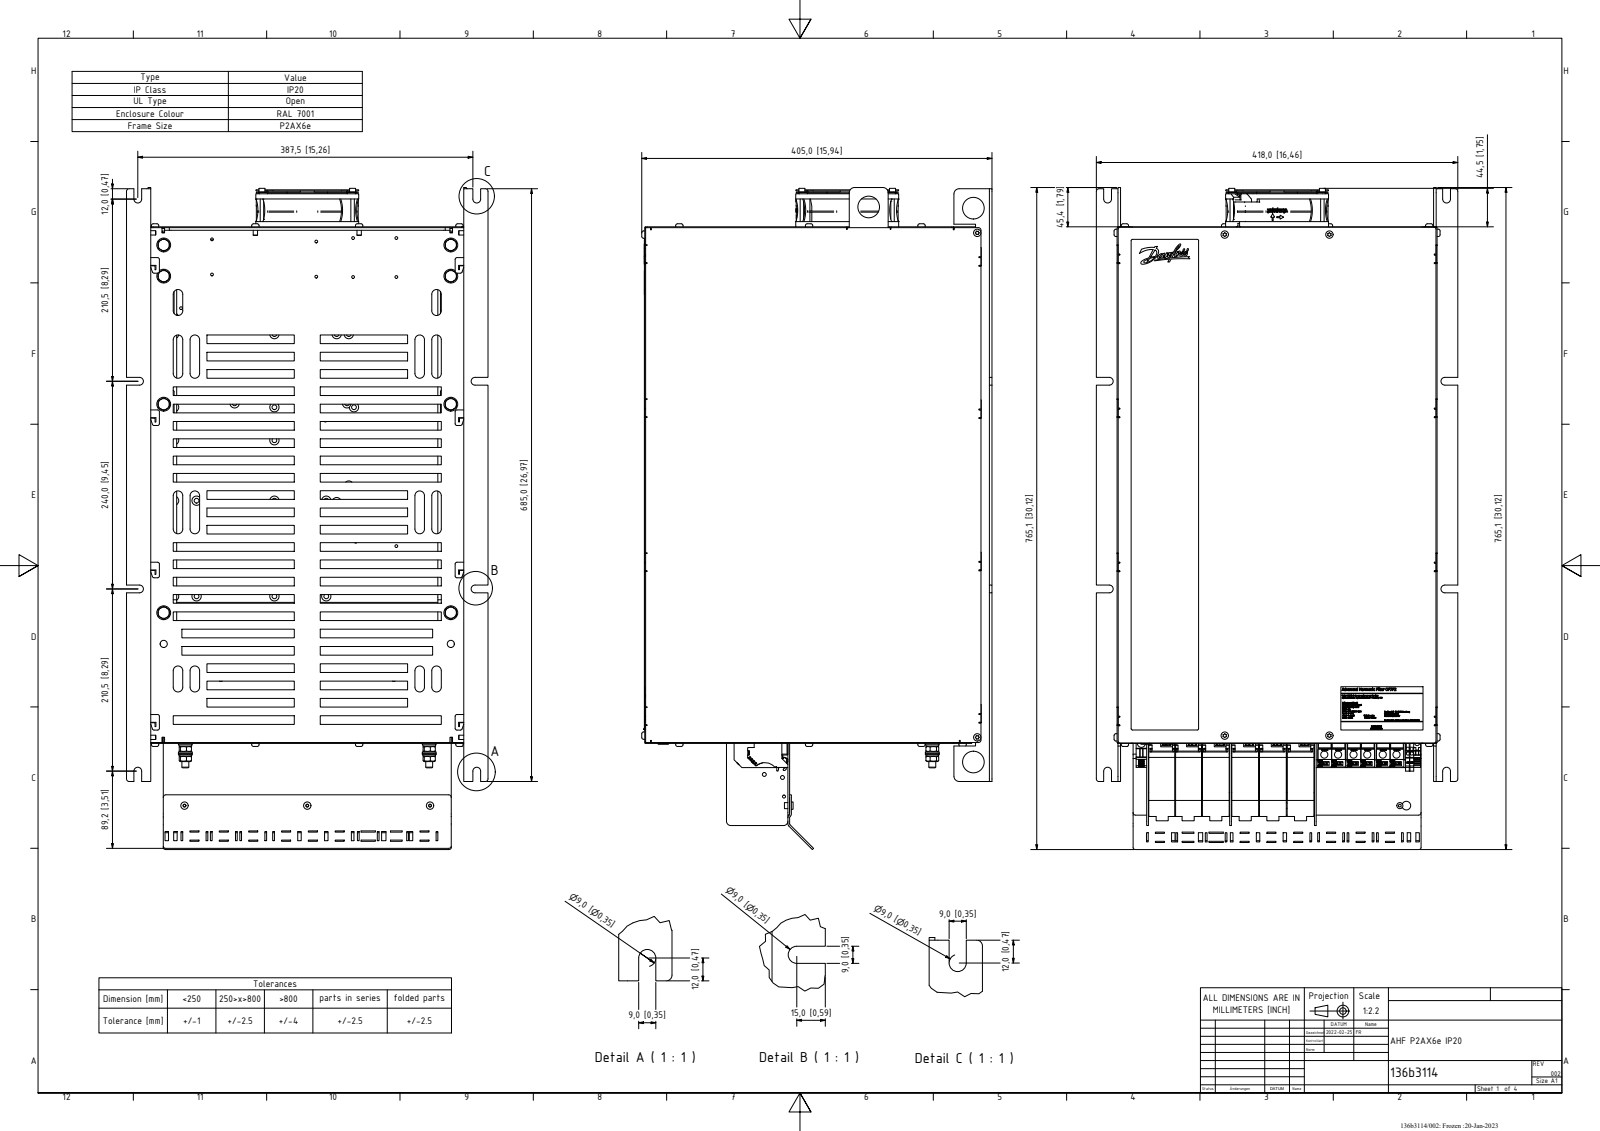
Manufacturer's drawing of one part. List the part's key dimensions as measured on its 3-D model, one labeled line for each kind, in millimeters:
Part name (STEP PRODUCT): X6_IP20_IF_OUT_2
STEP written by: CREO PARAMETRIC BY PTC INC, 2020342 (CONFIG_CONTROL_DESIGN)
Units: millimetres
Bodies: 3 solids, 2350 faces (1827 planar, 481 cylindrical, 42 other)
Overall size (bounding box): 765.06 × 510.36 × 505.91
Volume: 5 962 000 mm³ · Surface area: 2 780 000 mm²
Round holes (diameter × count): ⌀25 ×4, ⌀12.5 ×2, ⌀34 ×1, ⌀48 ×1, ⌀62 ×1, ⌀66.2 ×1, ⌀74.54 ×1, ⌀76 ×1, ⌀83 ×1, ⌀90 ×1, ⌀91.4 ×1, ⌀99.8 ×1
Round bosses / shafts (diameter × count): ⌀8.5 ×14, ⌀8 ×8, ⌀18 ×6, ⌀15.33 ×6, ⌀14.8 ×6, ⌀15.01 ×4, ⌀9 ×4, ⌀7 ×4
Partial cylindrical surfaces — rounded edges, fillets, slot ends (radius × count): R4.5 ×8, R1.29 ×1, R2.9 ×1, R3.69 ×1, R3.91 ×1, R4.27 ×1, R5.4 ×1, R6.76 ×1
Main face-to-face distances: 3, 367.17, 370.17, 364.17, 2, 372.17, 2.97, 375.14, 375.17, 378.14
Hole centre spacings: 159.01, 0.35, 121.06, 121.11, 248.98, 640, 652.72, 652.75
